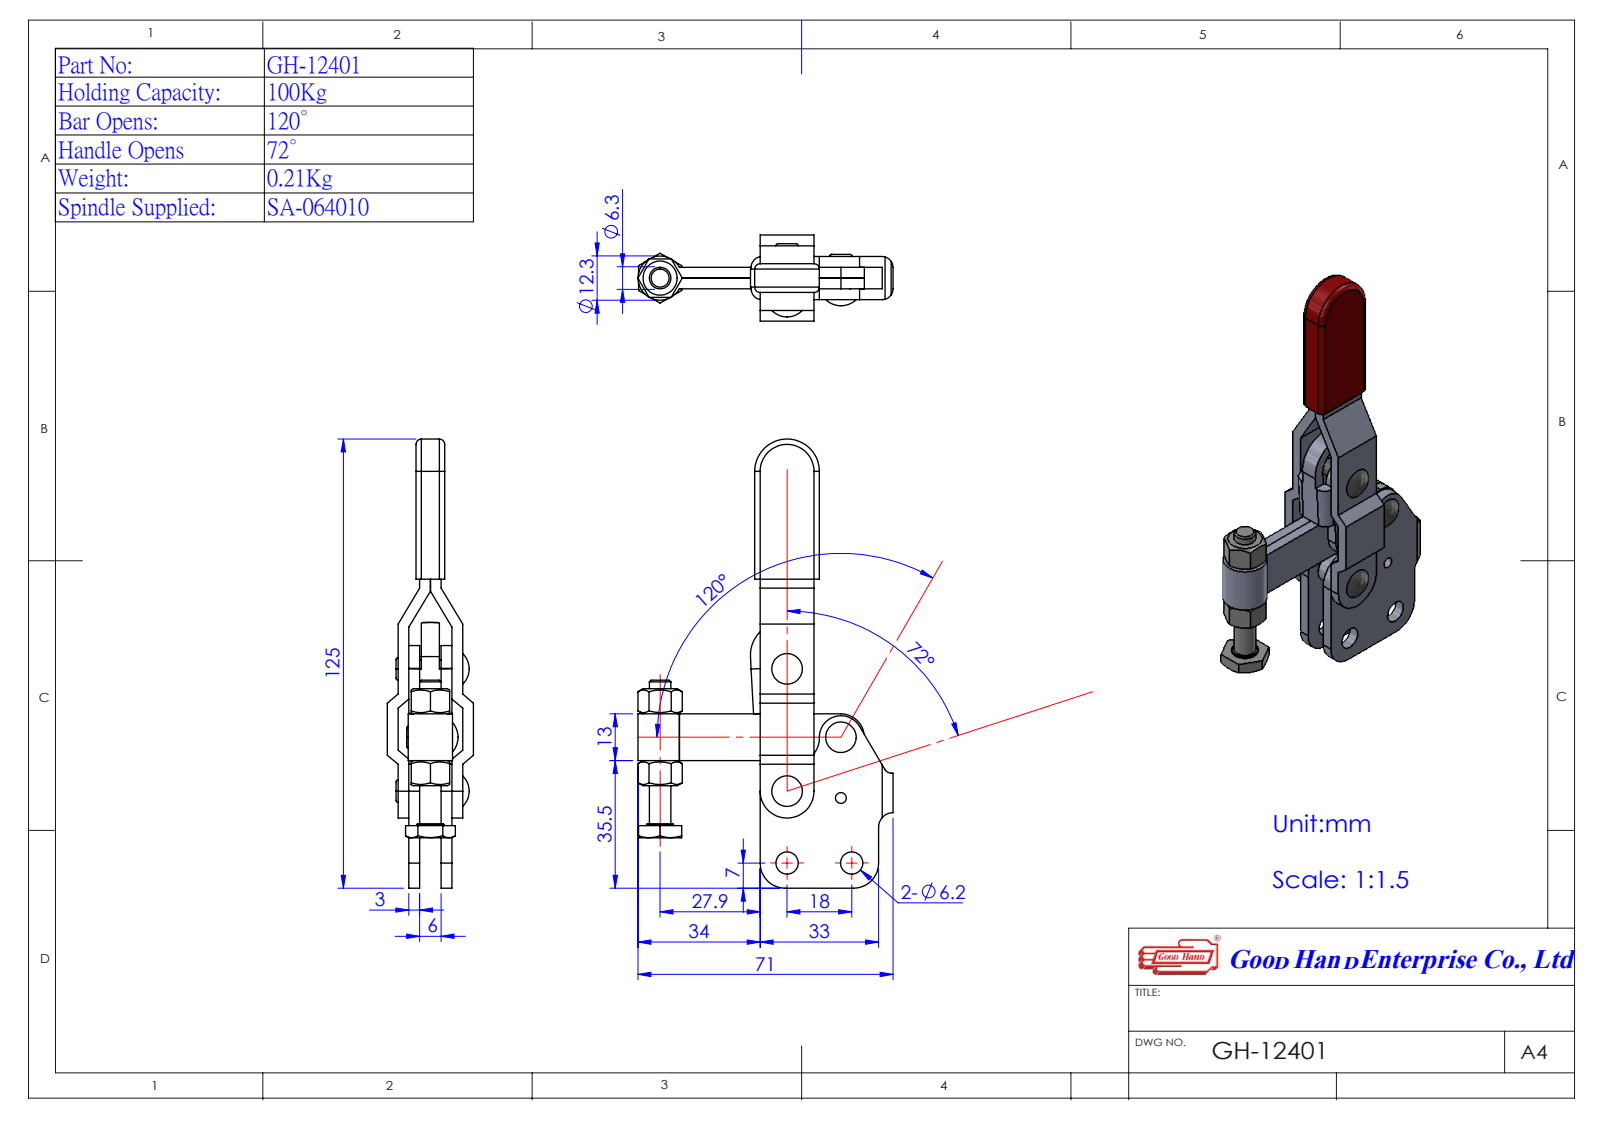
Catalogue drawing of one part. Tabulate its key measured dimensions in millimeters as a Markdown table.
| quantity | value |
| --- | --- |
| part name | GH-12401(簡化)-1; Group5^GH-12401(簡化)-1; Group2^GH-12401(簡化)-1; 11140108-1^GH-12401(簡化)-1 (+2 more) |
| STEP written by | SolidWorks 2016 (AUTOMOTIVE_DESIGN) |
| units | millimeters |
| bodies | 5 solids, 220 faces (99 planar, 89 cylindrical, 32 other) |
| overall size | 125 × 71.03 × 24 |
| volume | 29 673 mm³ |
| surface area | 21 782 mm² |
| round holes (diameter × count) | 3.5 × 4, 6.2 × 2, 3 × 1, 6.3 × 1 |
| round bosses / shafts (diameter × count) | 4.8 × 2, 12.3 × 1, 7.5 × 1, 6 × 1, 3.5 × 1 |
| partial cylindrical surfaces (radius × count) | 1.5 × 4, 3 × 4, 6.5 × 3, 1 × 2, 3.17 × 2, 7 × 2, 7.5 × 2, 2 × 1 |
| main face-to-face distances | 3, 6, 9, 12, 15, 13, 18, 7, 1, 4 |
| hole center spacings | 14, 15.03, 15.12, 16.9, 18, 18.35, 19.03, 20 |
